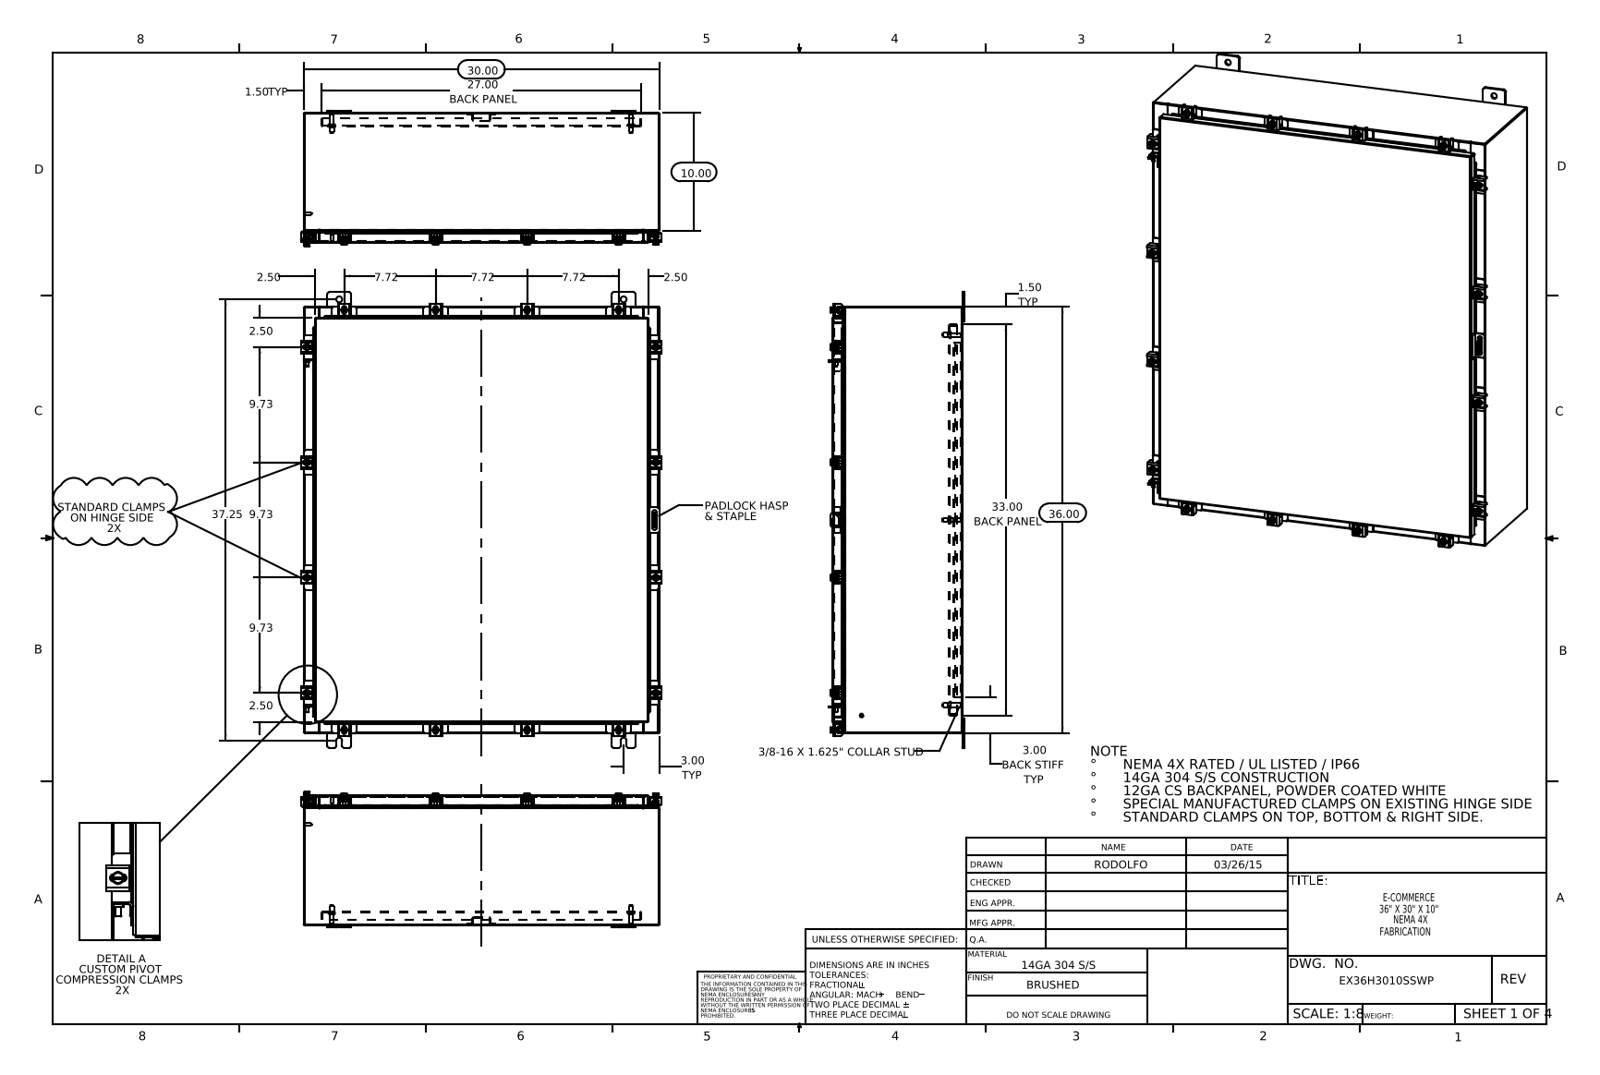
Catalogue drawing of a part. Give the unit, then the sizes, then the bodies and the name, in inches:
Units: inches
Overall size (bounding box): 38.5 × 30.421 × 11.453
Round holes (diameter × count): ⌀0.213 ×16, ⌀0.26 ×16, ⌀0.5 ×10, ⌀0.125 ×1, ⌀0.25 ×1
Round bosses / shafts (diameter × count): ⌀0.5 ×16, ⌀0.25 ×16, ⌀0.399 ×14, ⌀0.625 ×6, ⌀0.375 ×6, ⌀0.33 ×6, ⌀0.315 ×2, ⌀0.236 ×2
Partial cylindrical surfaces — rounded edges, fillets, slot ends (radius × count): R0.06 ×70, R0.141 ×32, R0.013 ×30, R0.12 ×30, R0.088 ×26, R0.19 ×24, R0.09 ×22, R0.05 ×21
Main face-to-face distances: 0.075, 10.9, 10.826, 10.975, 0.104, 1, 1.075, 9.826, 9.9, 1.179
Hole centre spacings: 31.017, 2.347, 4.44, 5.299, 9.73, 10.964, 13.241, 14.744
Volume: 401 in³ · Surface area: 9 968 in²
Bodies: 104 solids, 2594 faces (1371 planar, 1011 cylindrical, 212 other)
Part name (STEP PRODUCT): ATEX CLAMP HINGE BRAKET; EX36H3010SSWP; EX36H3010SSWP Padlock Hasp; EX36H3010SSWP Mounting Studs (+8 more)
STEP written by: SolidWorks 2014 (CONFIG_CONTROL_DESIGN)
